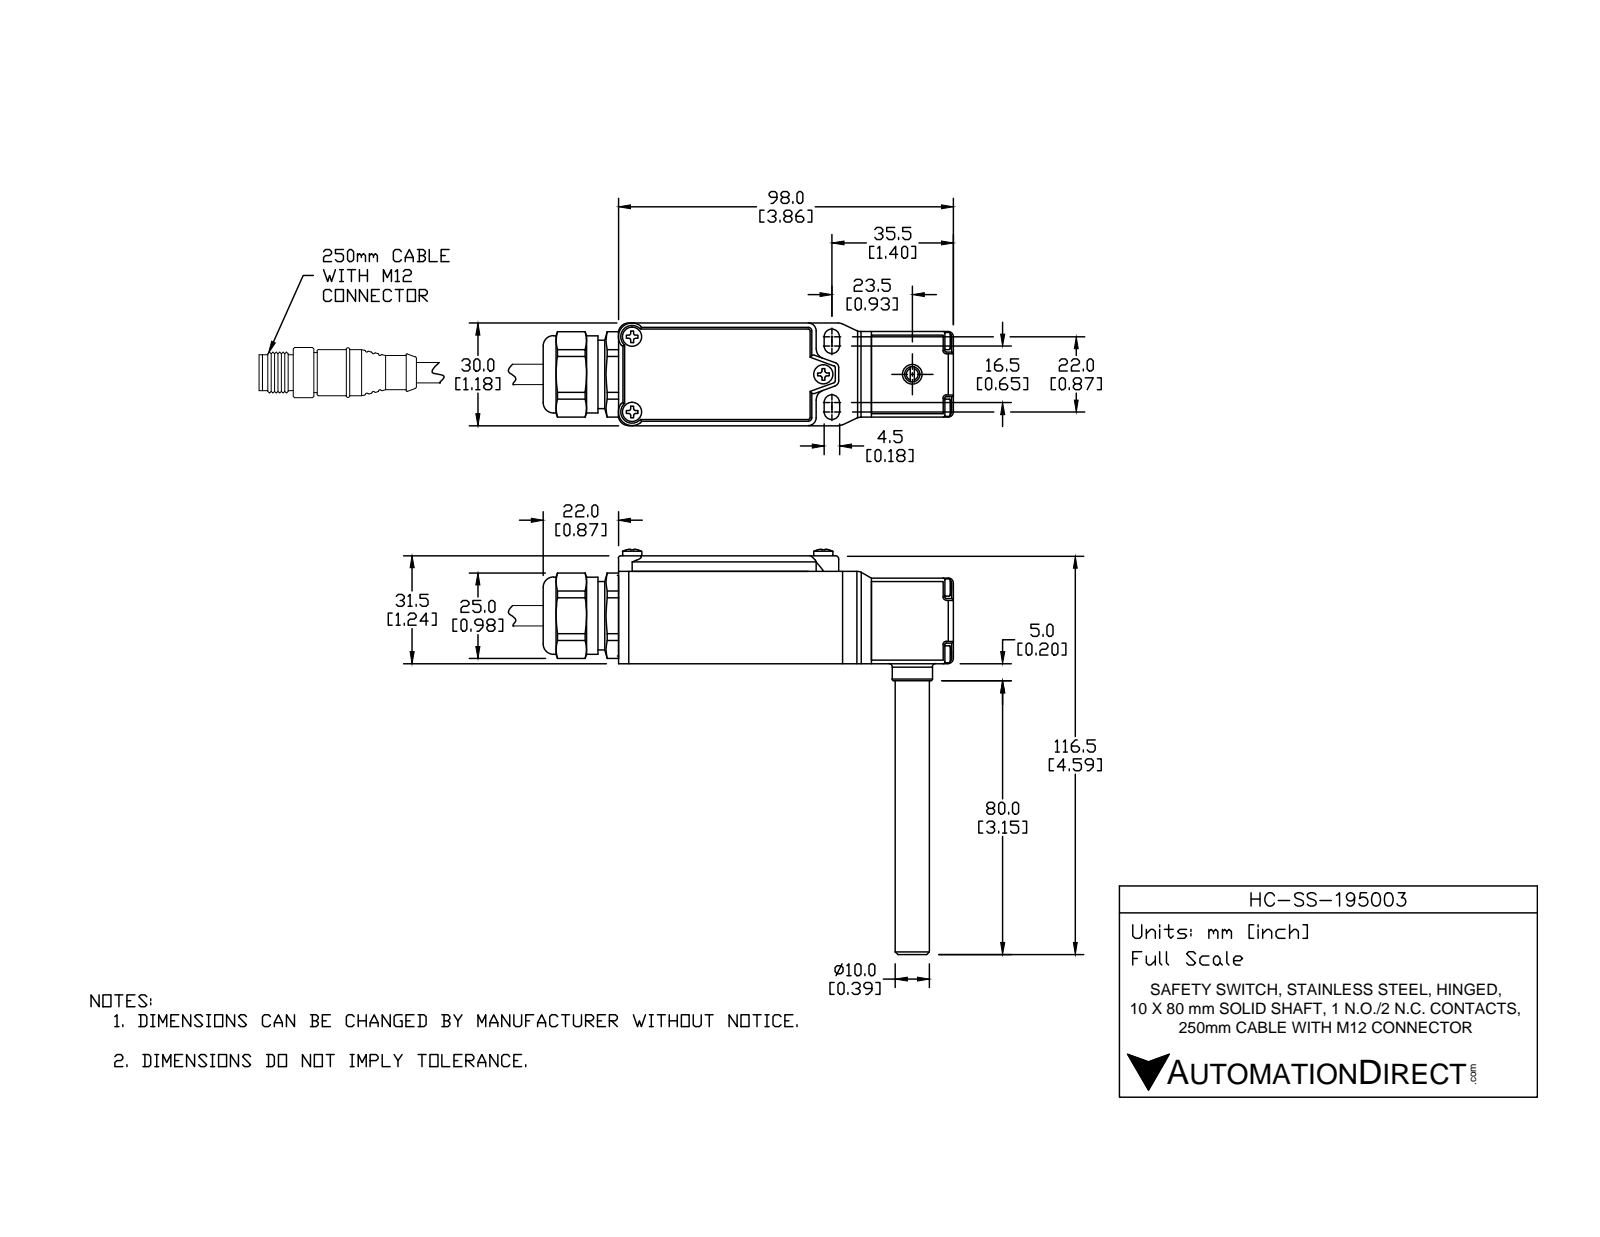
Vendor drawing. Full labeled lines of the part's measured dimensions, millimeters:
Part name (STEP PRODUCT): HC-SS-195003
STEP written by: SolidWorks 2014 (AUTOMOTIVE_DESIGN)
Units: millimetres
Bodies: 13 solids, 1168 faces (347 planar, 466 cylindrical, 355 other)
Overall size (bounding box): 118.4 × 99 × 30
Volume: 45 750 mm³ · Surface area: 35 130 mm²
Round holes (diameter × count): ⌀2.5 ×8, ⌀3.2 ×7, ⌀4 ×3, ⌀1.5 ×2, ⌀1.8 ×2, ⌀2.2 ×2, ⌀3.6 ×2, ⌀2.1 ×1, ⌀2.9 ×1, ⌀4.4 ×1, ⌀4.7 ×1, ⌀5.5 ×1
Round bosses / shafts (diameter × count): ⌀3 ×7, ⌀5 ×5, ⌀3.5 ×4, ⌀5.6 ×3, ⌀23.5 ×1, ⌀17.7 ×1, ⌀10 ×1, ⌀9.8 ×1
Partial cylindrical surfaces — rounded edges, fillets, slot ends (radius × count): R0.5 ×175, R1 ×20, R0.3 ×18, R0.2 ×14, R0.7 ×8, R3 ×8, R1.5 ×6, R2.3 ×4
Main face-to-face distances: 2.5, 29, 2, 2.9, 27.1, 30, 4.5, 31.5, 0.4, 27.5
Hole centre spacings: 13.8, 19.5, 4.7, 6.2, 10.5, 10.7, 10.8, 12.1
